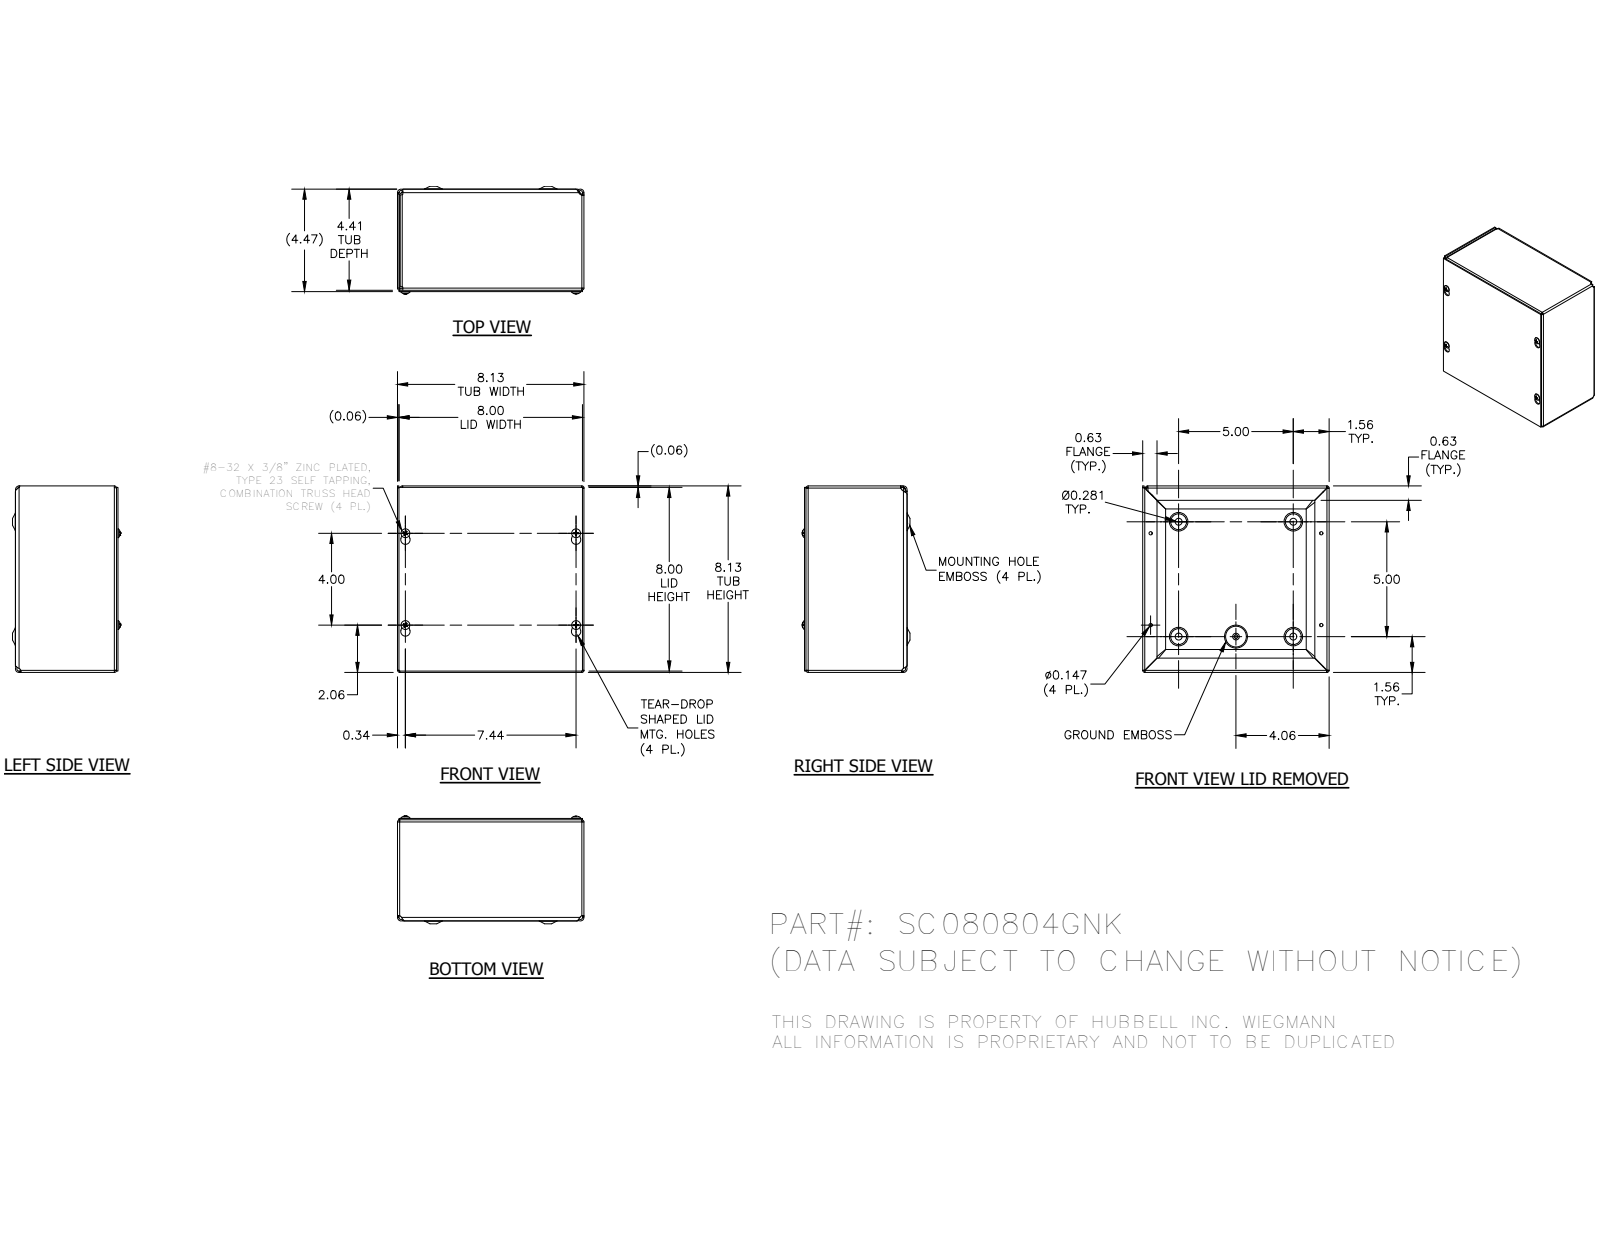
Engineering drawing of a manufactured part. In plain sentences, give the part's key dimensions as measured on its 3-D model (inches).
The part is named "SC0808GNKBKP; SC080804GNKWRA; SC0808GNKLID; 34056 (+1 more)". Its 3-D file was written by "Autodesk Inventor 2014 (AUTOMOTIVE_DESIGN)". It is 7 solids with 358 faces: 133 planar, 73 cylindrical and 152 other. Overall it measures 8.125 by 8.125 by 4.693 inches. Its volume is 19.03 cubic inches and its surface area 623.5 square inches. Round holes: 4 of diameter 0.147, 4 of diameter 0.3, 1 of diameter 0.165. Round bosses or shafts: 4 of diameter 0.384, 4 of diameter 0.164, 1 of diameter 0.228. Partial cylindrical surfaces (rounded edges, fillets, slot ends): 8 of radius 0.031, 8 of radius 0.093, 4 of radius 0.055, 4 of radius 0.062, 4 of radius 0.094, 4 of radius 0.117, 4 of radius 0.124, 4 of radius 0.125. The main face-to-face distances are 0.062, 8.063, 4.343, 8.001, 4.405, 0.063, 4.406, 4.468, 0.062, 8.125. The hole center spacings are 5, 1.317, 2.5, 4, 4.661, 4.663, 5.59, 6.239.
